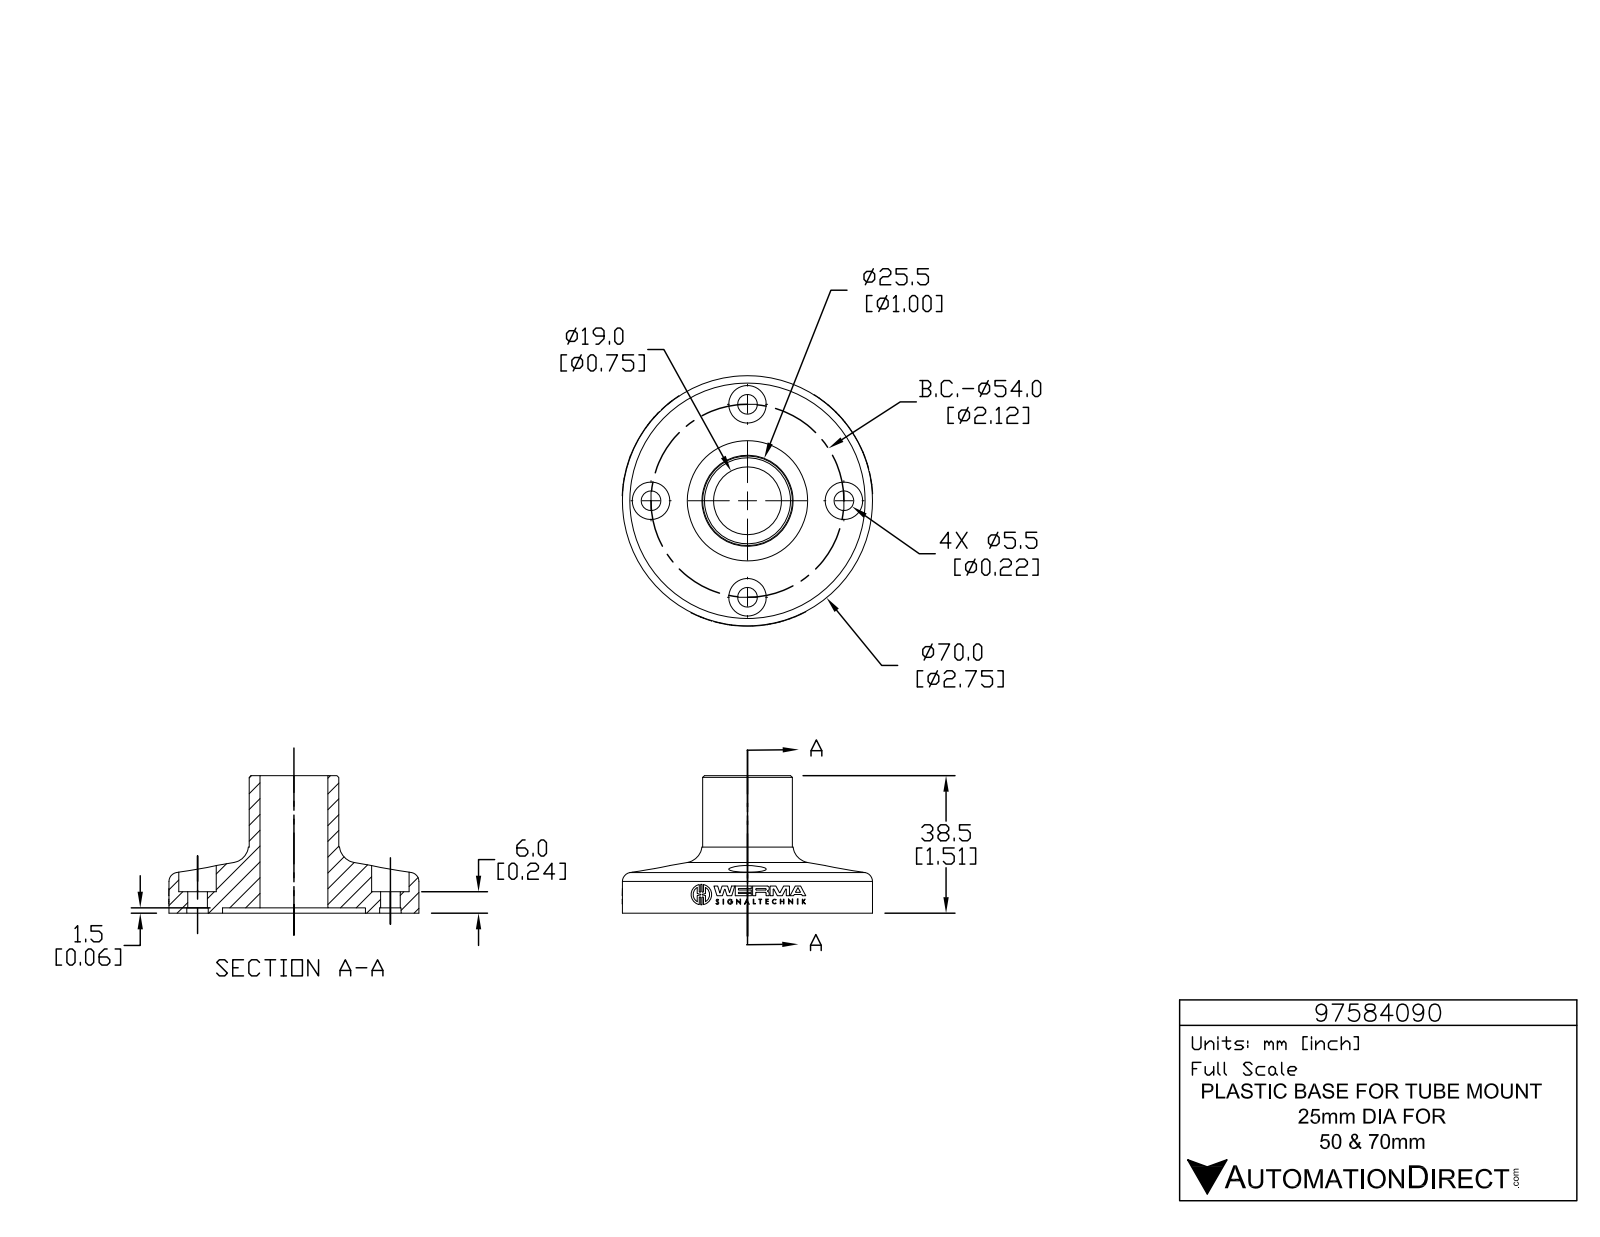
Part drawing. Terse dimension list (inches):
name: 97584090
written by: SolidWorks 2015 (AUTOMOTIVE_DESIGN)
unit: in
bodies: 1 solid, 808 faces (531 planar, 269 cylindrical, 8 other)
size: 2.76 × 2.76 × 1.516
volume: 2.839 in³; area: 22.82 in²
holes: 4× ⌀0.217, 4× ⌀0.236, 4× ⌀0.413, 3× ⌀0.039, 1× ⌀0.748, 1× ⌀1.575
bosses: 3× ⌀0.226, 3× ⌀0.056, 1× ⌀2.756, 1× ⌀0.988
rounds: 6× R0.008, 6× R0.008, 6× R0.008, 6× R0.131, 3× R0.004, 3× R0.005, 3× R0.008, 3× R0.008
face distances: 0.059, 0.177, 0.236, 1.28, 1.457, 1.516, 0.787, 0.492, 0.669, 0.728
hole spacings: 1.063, 1.503, 2.126
